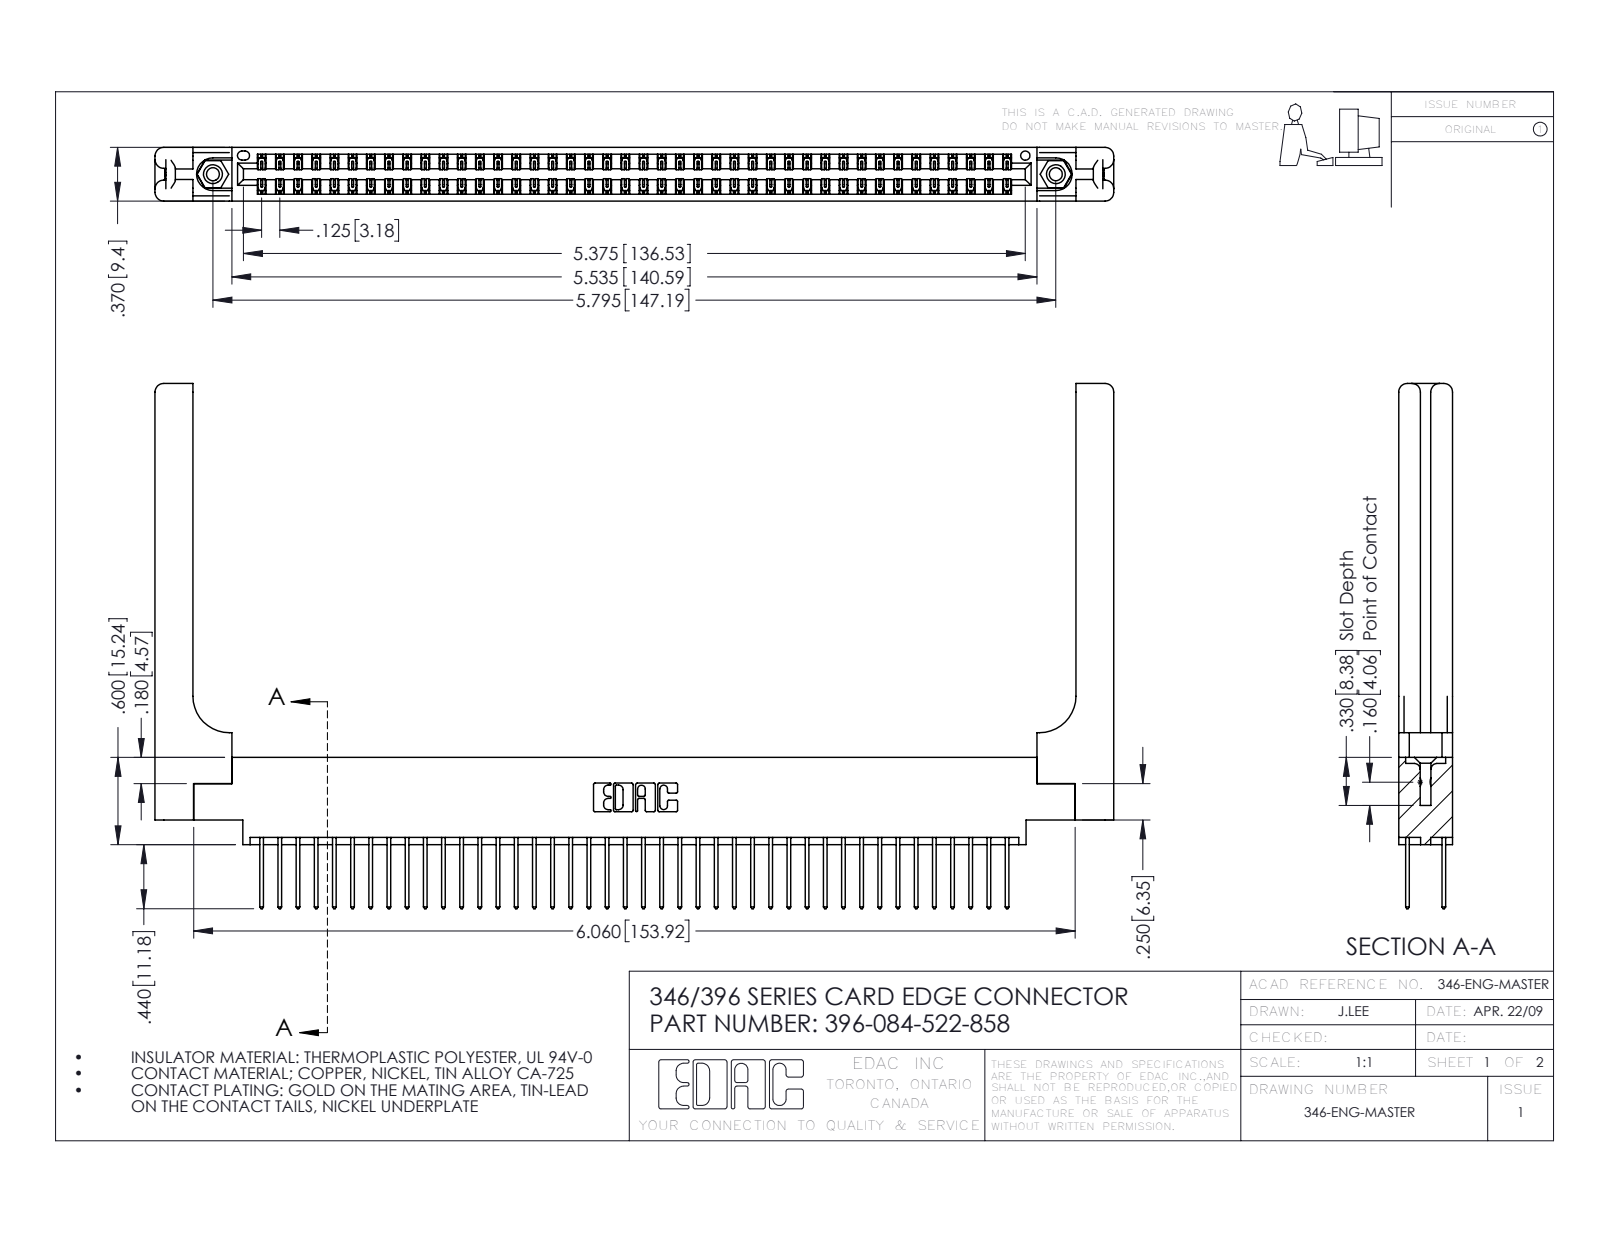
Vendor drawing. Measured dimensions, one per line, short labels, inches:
name: 346-220-058_345-220-058; 396-084-522-858; 346 Part_0.170 Offset - 0.156 Dia-TH; 345-250-001_345-250-001-102 (+1 more)
written by: SolidWorks 2016 (CONFIG_CONTROL_DESIGN)
unit: in
bodies: 89 solids, 4750 faces (3168 planar, 1522 cylindrical, 60 other)
size: 6.591 × 3.61 × 0.37
volume: 1.457 in³; area: 44.44 in²
holes: 2× ⌀0.089, 2× ⌀0.125, 2× ⌀0.156, 1× ⌀0.064
bosses: 2× ⌀0.155
rounds: 126× R0.006, 84× R0.01, 22× R0.01, 16× R0.06, 6× R0.007, 6× R0.031, 3× R0.026, 2× R0.014
face distances: 0.048, 0.322, 0.37, 0.072, 0.25, 0.025, 0.298, 0.148, 0.15, 0.275
hole spacings: 0.246, 5.586, 5.795
